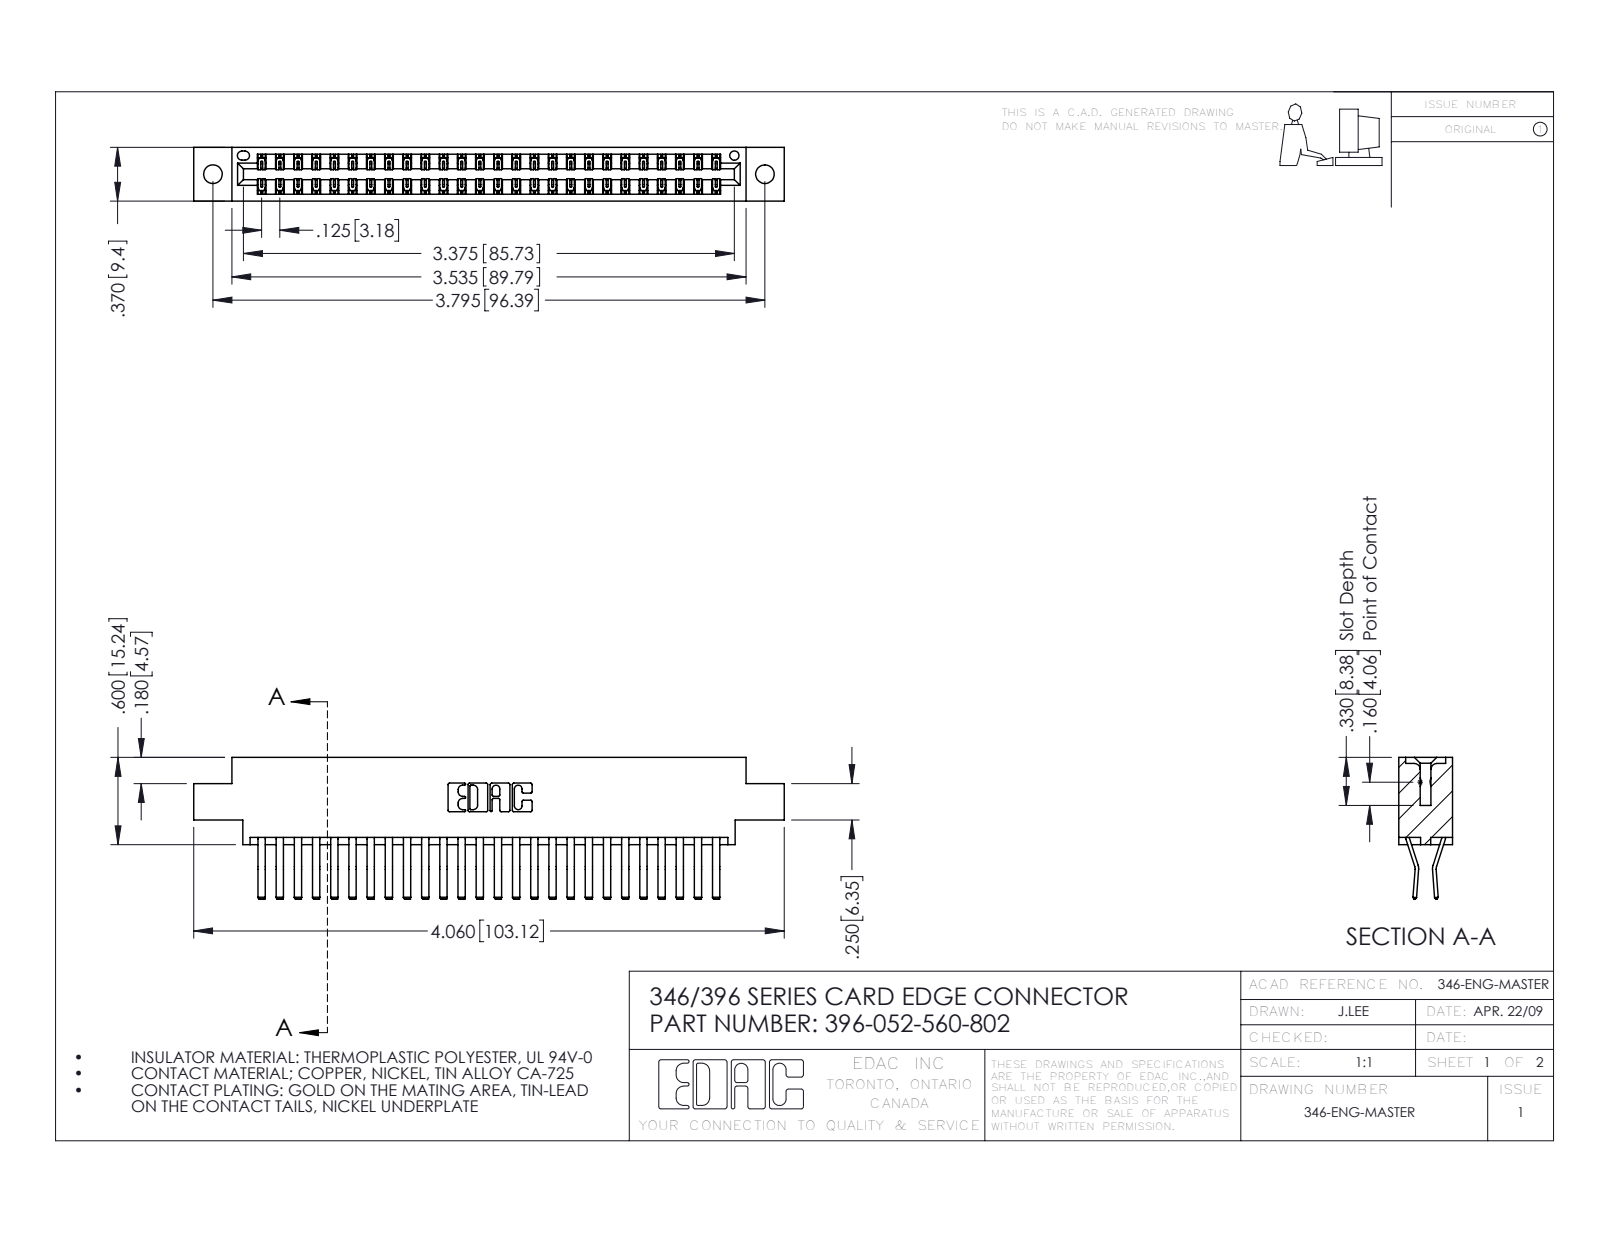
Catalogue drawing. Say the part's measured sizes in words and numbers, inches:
The part is named "345-292-001_560 Tail; 346 Part_0.170 Offset - 0.128 Dia; 396-052-560-802". Its 3-D file was written by "SolidWorks 2016 (CONFIG_CONTROL_DESIGN)". It is 53 solids with 2934 faces: 1900 planar, 1034 cylindrical and 0 other. Overall it measures 4.06 by 0.975 by 0.37 inches. Its volume is 0.615 cubic inches and its surface area 22.36 square inches. Round holes: 2 of diameter 0.128, 1 of diameter 0.064. Partial cylindrical surfaces (rounded edges, fillets, slot ends): 78 of radius 0.006, 22 of radius 0.01, 6 of radius 0.007, 6 of radius 0.031, 3 of radius 0.026, 2 of radius 0.01, 2 of radius 0.014, 2 of radius 0.022. The main face-to-face distances are 0.048, 0.322, 0.37, 0.25, 0.025, 0.072, 0.298, 0.275, 0.148, 0.222. The hole center spacings are 0.246, 3.587, 3.795.
